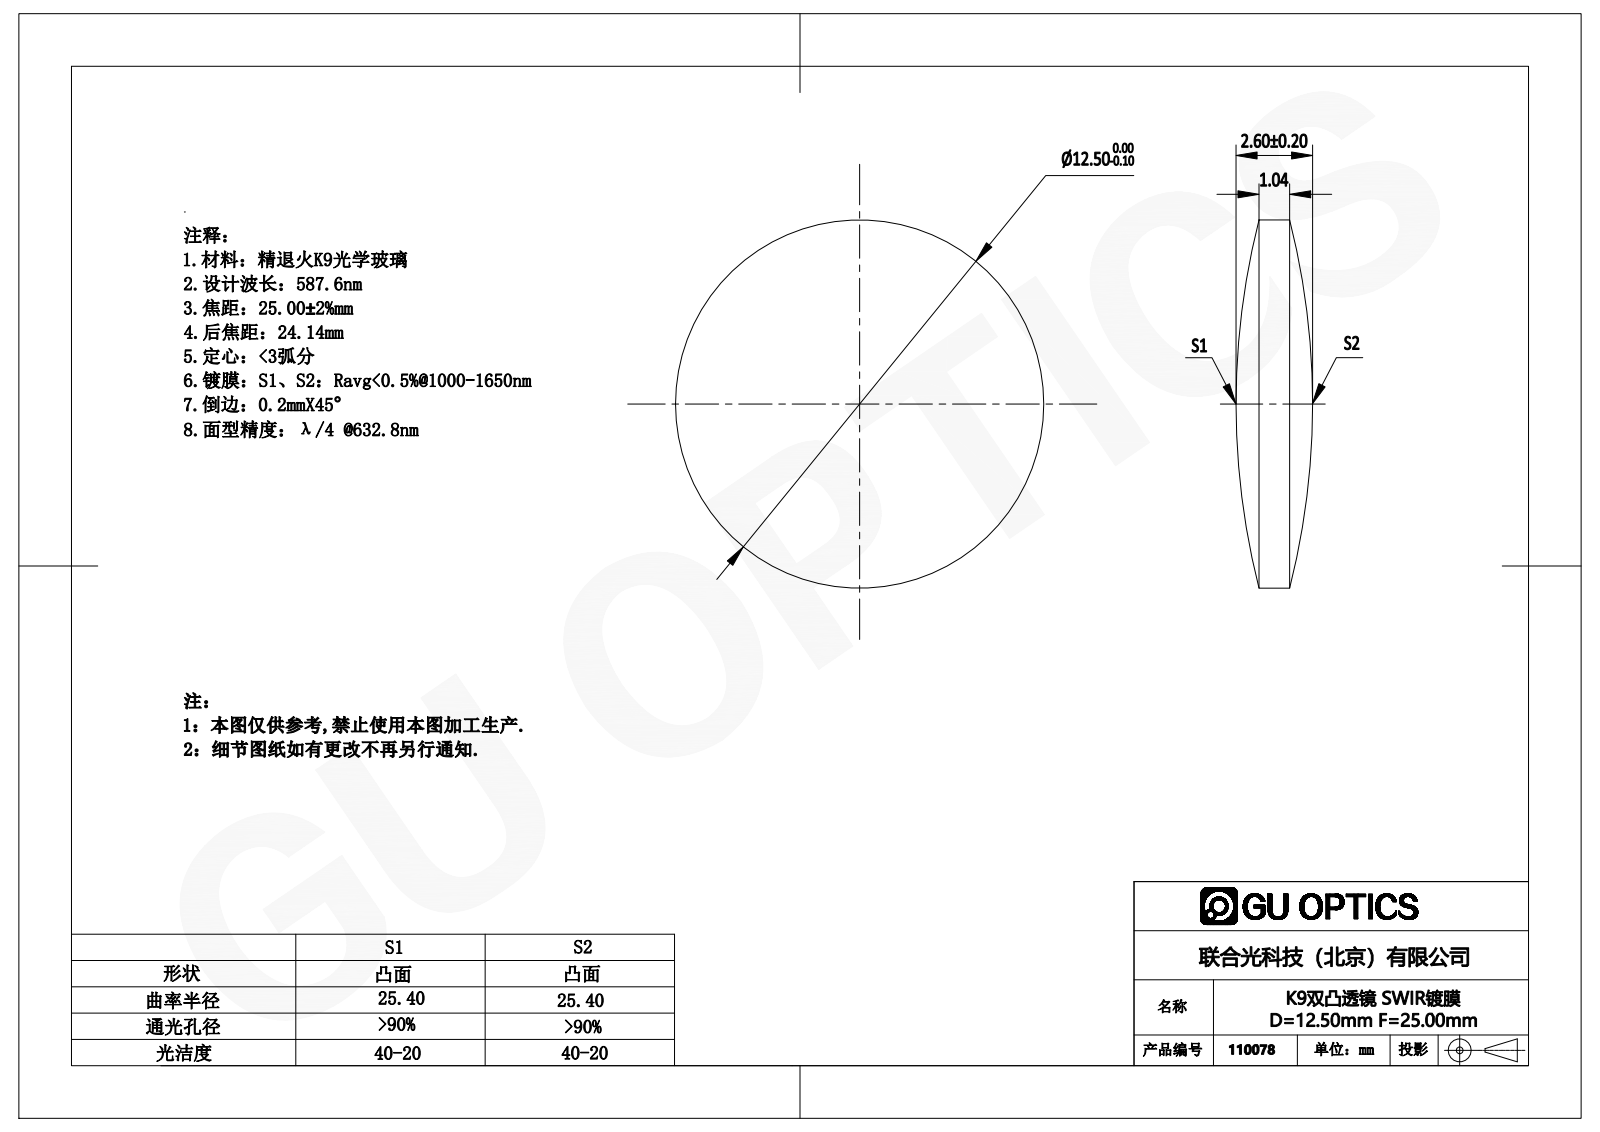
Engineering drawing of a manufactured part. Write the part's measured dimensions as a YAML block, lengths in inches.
part_name: "110012"
step_written_by: "SolidWorks 2016 (CONFIG_CONTROL_DESIGN)"
units: inches
bodies: {solids: 1, faces: 6, planar: 0, cylindrical: 2, other: 4}
overall_size: [0.492, 0.492, 0.102]
volume: 0.014
surface_area: 0.45
round_bosses_or_shafts:
  - {diameter: 0.492, count: 1}
